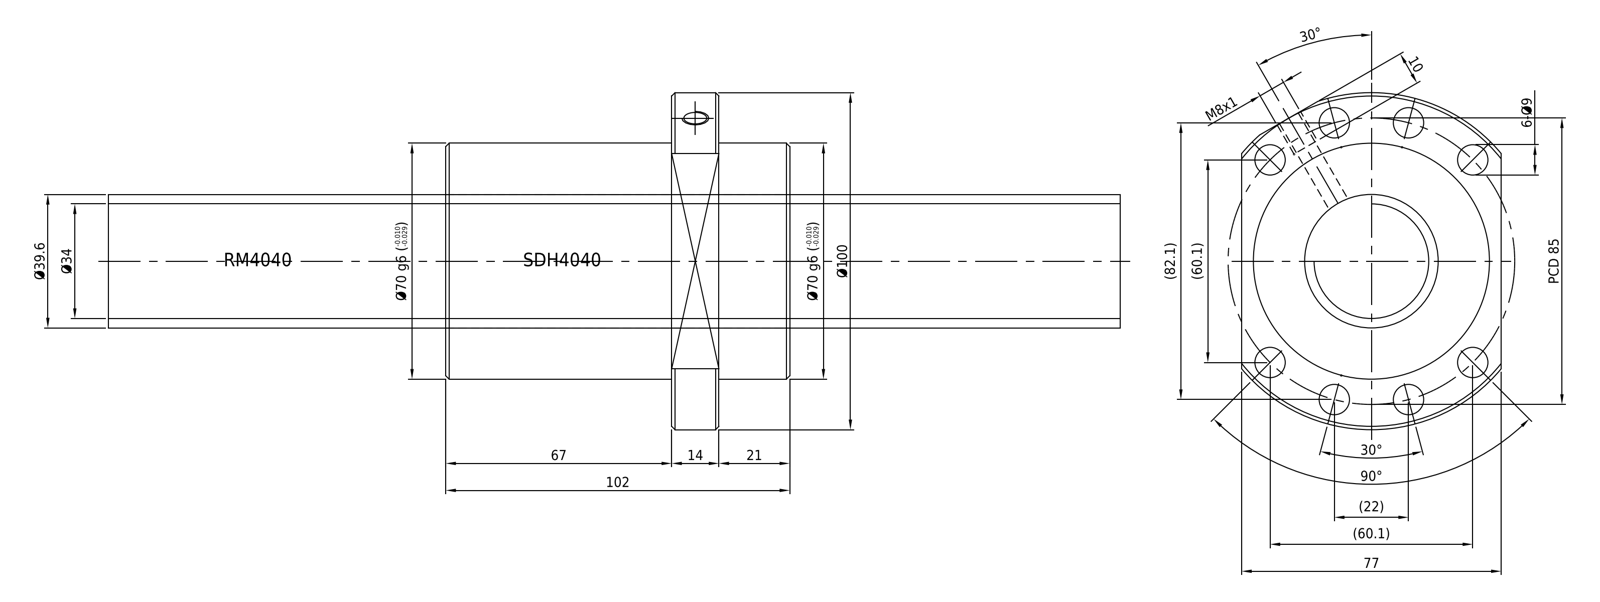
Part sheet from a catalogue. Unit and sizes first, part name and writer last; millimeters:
Units: millimetres
Overall size (bounding box): 300 × 100 × 77
Round holes (diameter × count): ⌀9 ×8, ⌀3 ×1, ⌀6.8 ×1, ⌀40 ×1
Round bosses / shafts (diameter × count): ⌀70 ×1, ⌀39.6 ×1
Partial cylindrical surfaces — rounded edges, fillets, slot ends (radius × count): R50 ×1
Main face-to-face distances: 99, 201, 102, 35, 67, 21, 14, 81, 120, 134
Hole centre spacings: 42.5, 22, 82.11, 73.62, 42.51, 60.1, 60.11, 85
Volume: 667 501 mm³ · Surface area: 89 502 mm²
Bodies: 2 solids, 52 faces (9 planar, 31 cylindrical, 12 other)
Part name (STEP PRODUCT): SDH4040; RM4040
STEP written by: SolidWorks 2013 (CONFIG_CONTROL_DESIGN)
